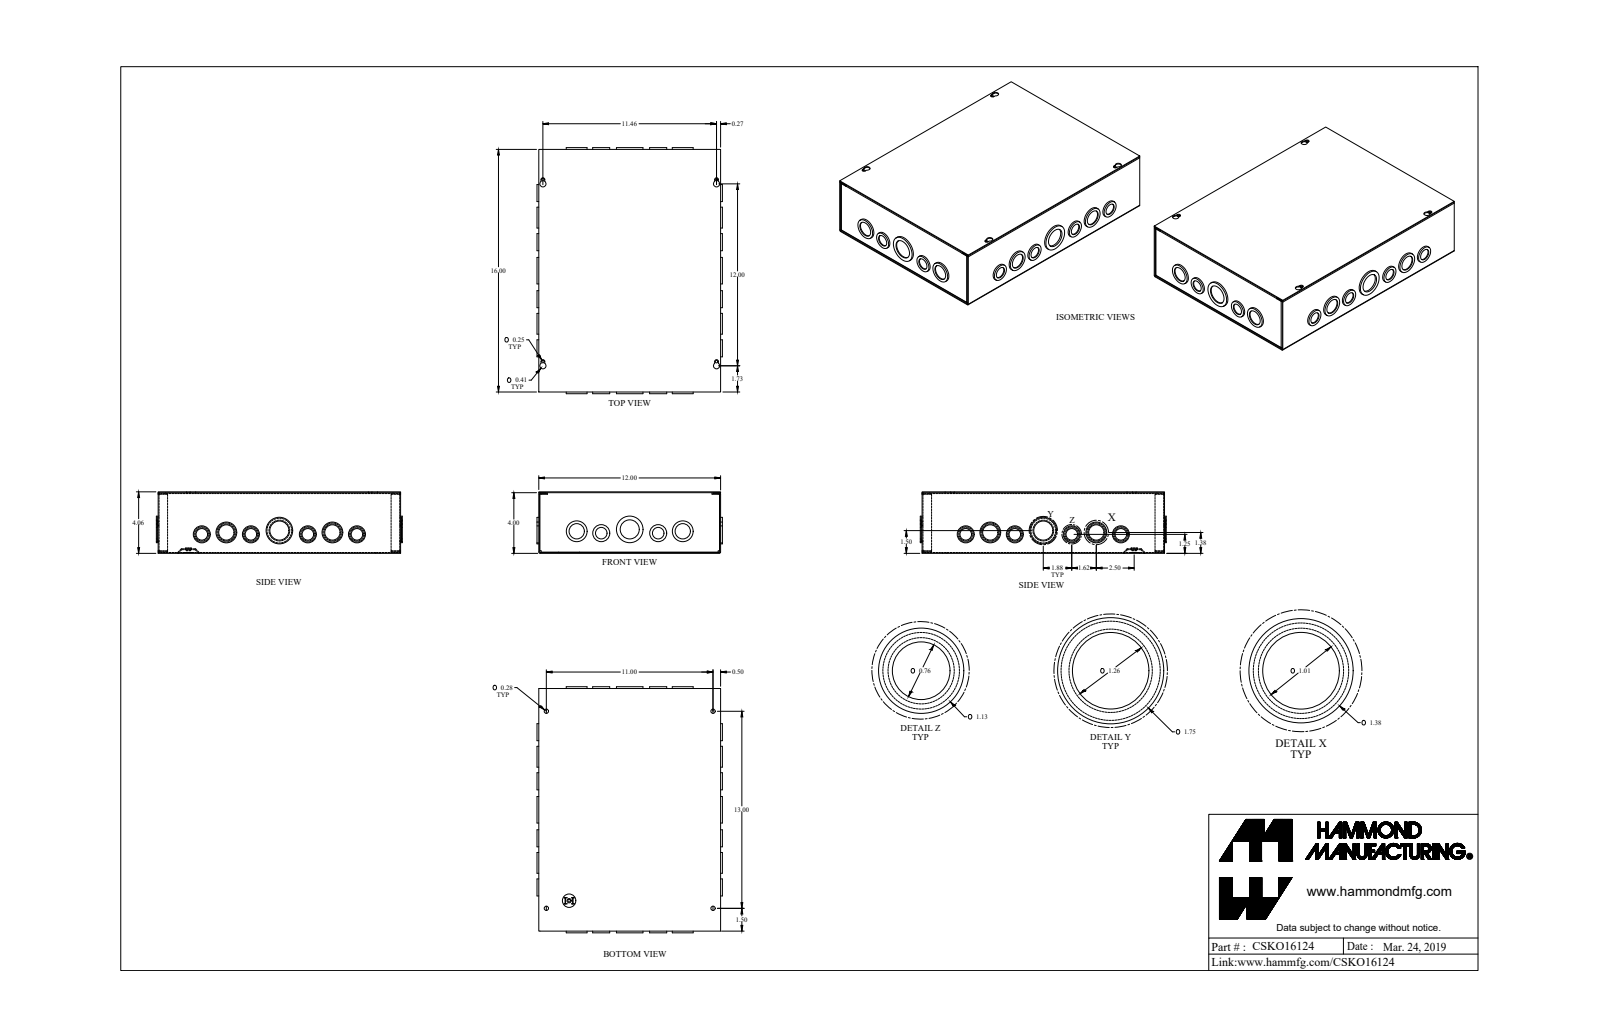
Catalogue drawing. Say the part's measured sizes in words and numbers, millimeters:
The part is named "CSKO16124_Default". Its 3-D file was written by "SolidWorks 2019 (CONFIG_CONTROL_DESIGN)". It is 4 solids with 493 faces: 221 planar, 264 cylindrical and 8 other. Overall it measures 412.3 by 310.7 by 103 millimeters. Its volume is 617 300 cubic millimeters and its surface area 860 600 square millimeters. Round holes: 10 of diameter 25.7, 6 of diameter 19.3, 6 of diameter 32, 5 of diameter 4.3, 4 of diameter 7.1, 2 of diameter 41.6, 1 of diameter 12.7. Round bosses or shafts: 8 of diameter 28.6, 6 of diameter 22.2, 5 of diameter 34.9, 4 of diameter 22.2, 2 of diameter 44.5, 2 of diameter 28.6, 1 of diameter 34.9, 1 of diameter 12.5. Partial cylindrical surfaces (rounded edges, fillets, slot ends): 12 of radius 0.7, 12 of radius 2.2, 8 of radius 1.4, 4 of radius 3.2, 4 of radius 5.2. The main face-to-face distances are 1.4, 101.6, 100.2, 103, 303.4, 405, 304.8, 301.9, 406.4, 403.5. The hole center spacings are 41.3, 14, 48.2, 89, 136.7, 177.8, 285.5, 317.6.
